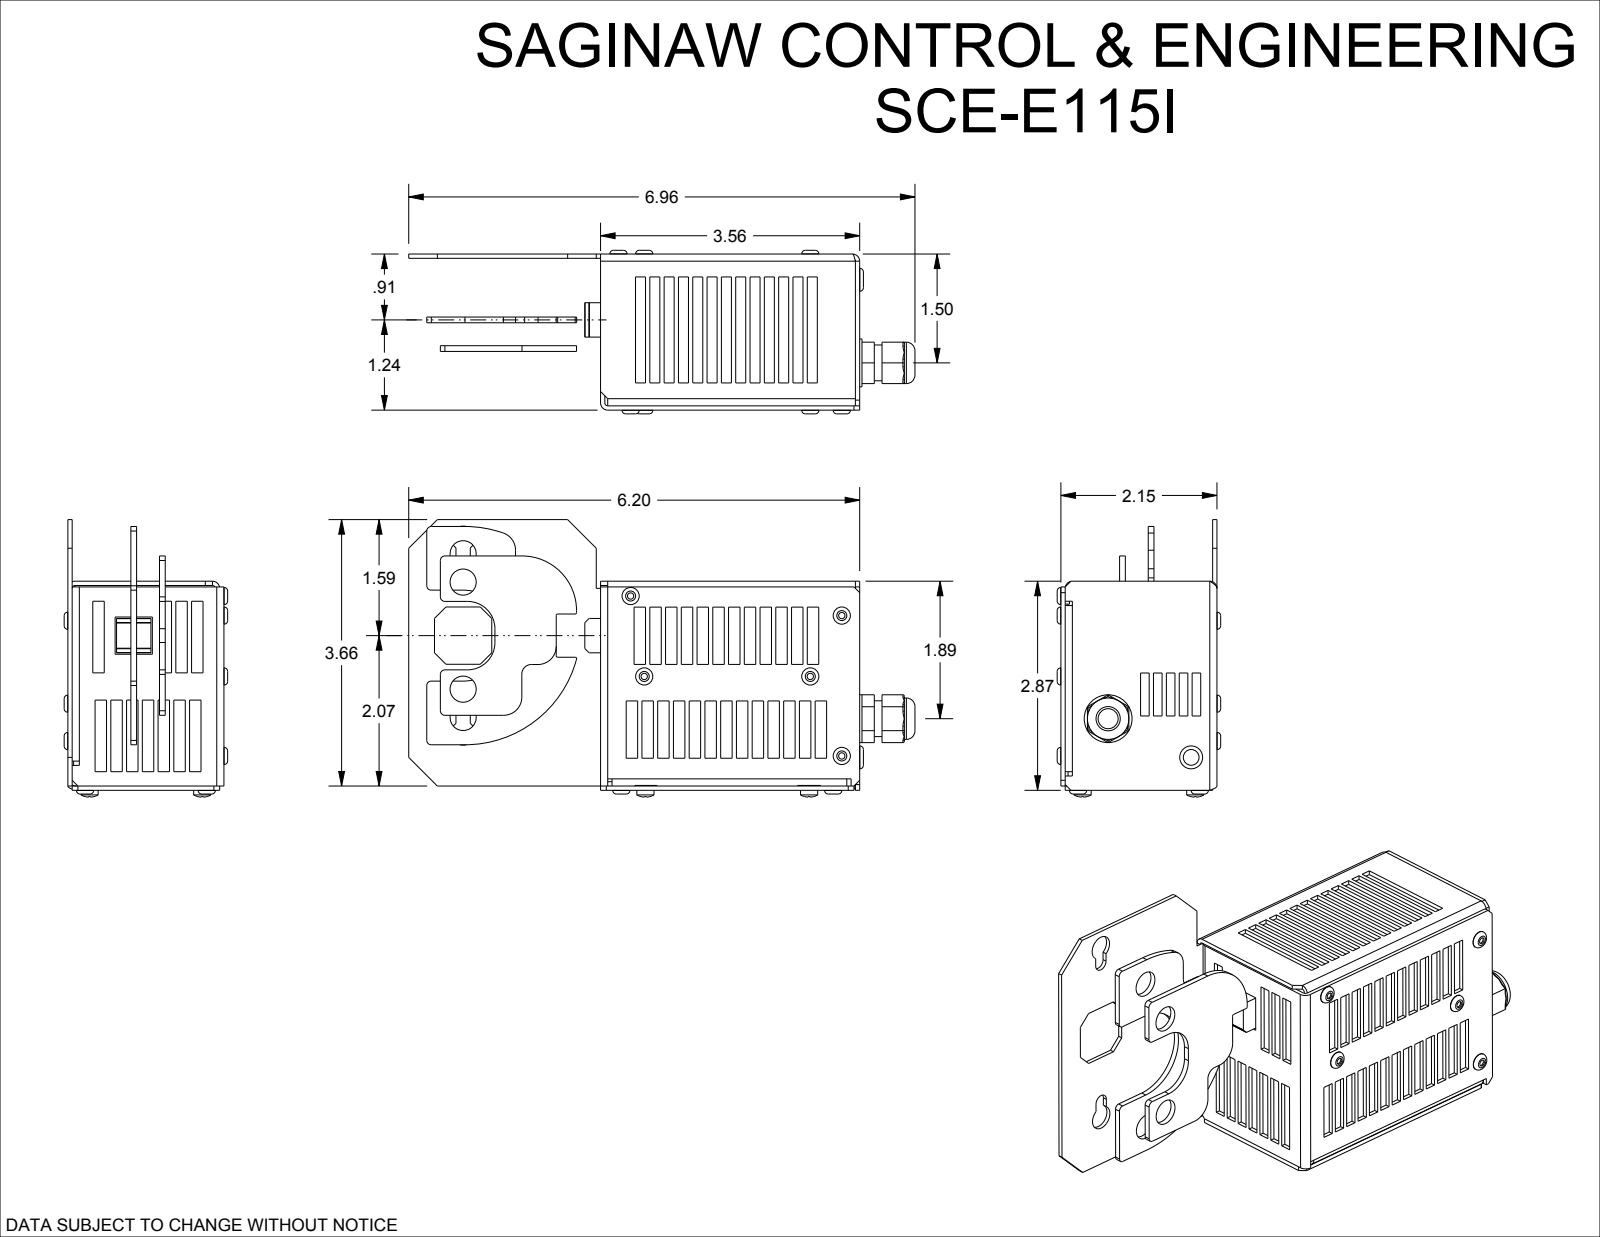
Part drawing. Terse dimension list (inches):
name: SCE-E115I
written by: SolidWorks 2019 (CONFIG_CONTROL_DESIGN)
unit: in
bodies: 25 solids, 877 faces (679 planar, 150 cylindrical, 48 other)
size: 6.961 × 3.814 × 2.248
volume: 20 in³; area: 165.9 in²
holes: 17× ⌀0.126, 13× ⌀0.087, 4× ⌀0.359, 2× ⌀0.331, 1× ⌀0.177, 1× ⌀0.276, 1× ⌀0.492
bosses: 17× ⌀0.236, 17× ⌀0.118, 4× ⌀0.098, 1× ⌀0.657, 1× ⌀0.569, 1× ⌀0.472, 1× ⌀0.315, 1× ⌀0.157
rounds: 9× R0.098, 7× R0.039, 6× R0.02, 5× R0.063, 4× R0.01, 4× R0.02, 4× R0.25, 3× R0.06
face distances: 0.059, 0.118, 0.079, 0.177, 2.087, 1.969, 2.028, 1.909, 0.02, 1.89
hole spacings: 0.337, 1.645, 2.583, 3.043, 0.374, 0.604, 1.55, 1.673
